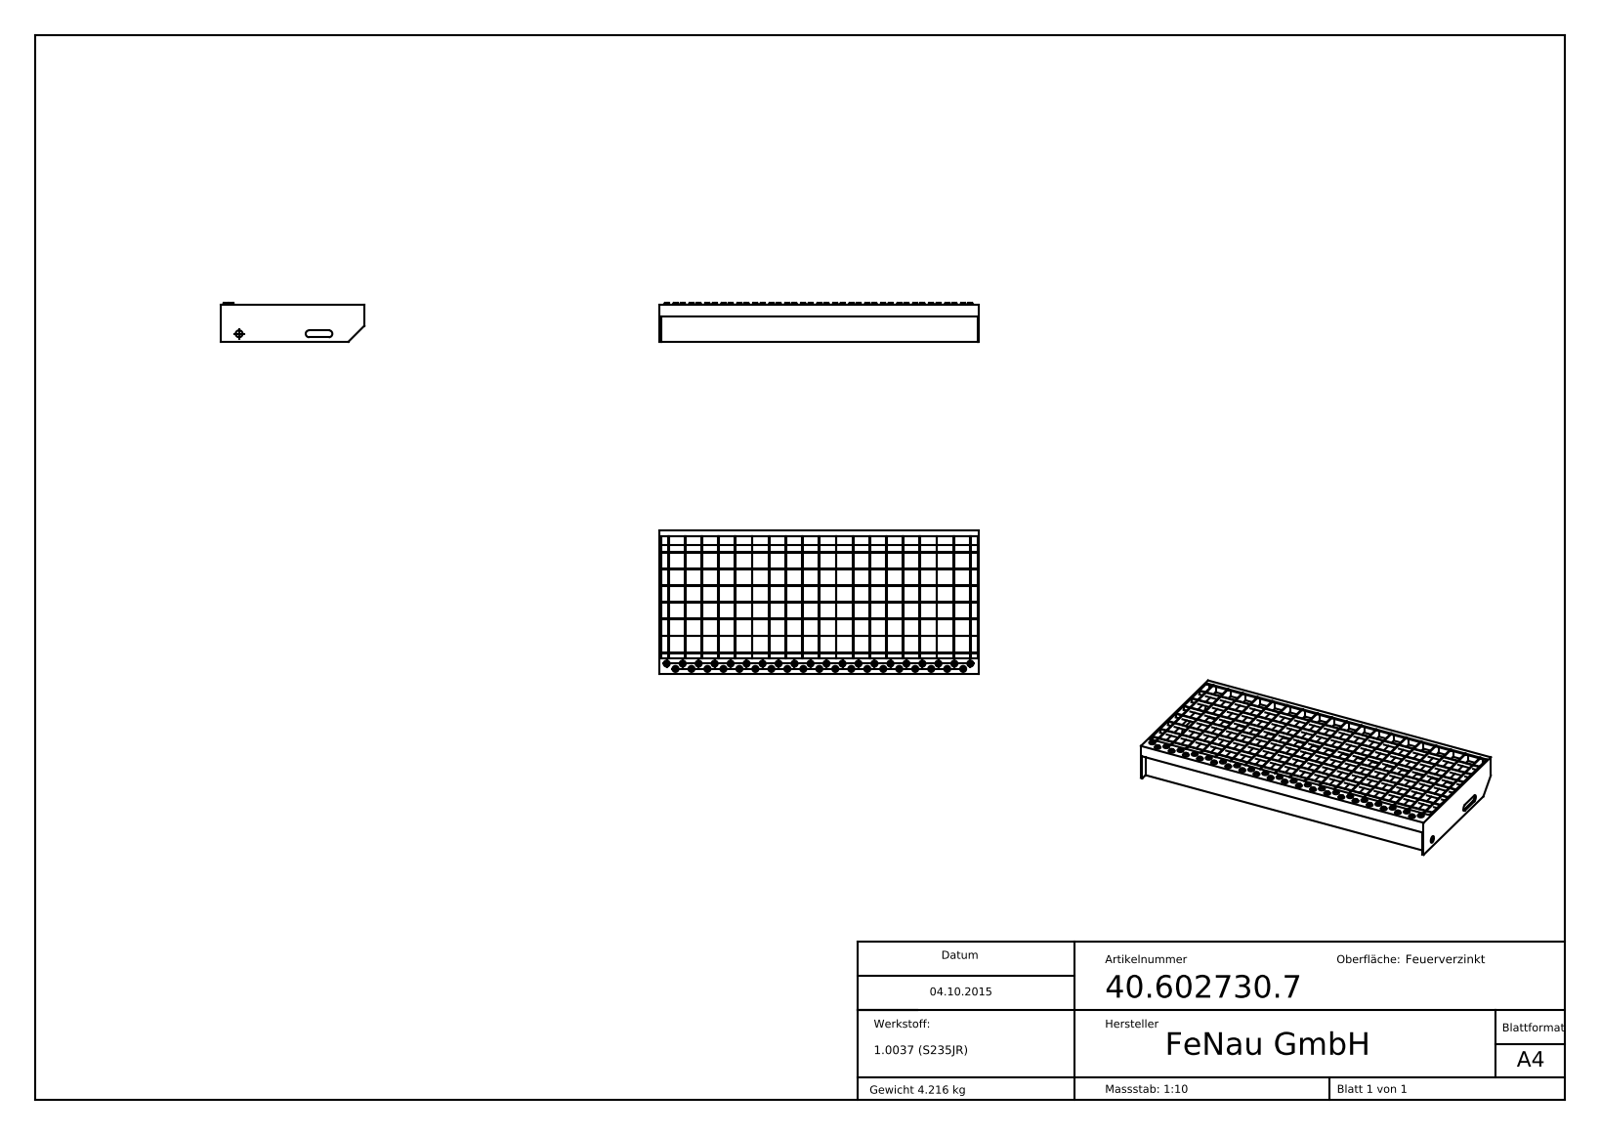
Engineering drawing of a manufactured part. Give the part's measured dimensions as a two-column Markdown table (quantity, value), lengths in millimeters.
| quantity | value |
| --- | --- |
| part name | 40.602730.7 |
| STEP written by | SolidWorks 2015 (CONFIG_CONTROL_DESIGN) |
| units | millimeters |
| bodies | 18 solids, 667 faces (412 planar, 88 cylindrical, 167 other) |
| overall size | 600 × 270 × 72.67 |
| volume | 540 534 mm³ |
| surface area | 609 199 mm² |
| round holes (diameter × count) | 7 × 39, 13 × 1 |
| partial cylindrical surfaces (radius × count) | 6.5 × 2 |
| main face-to-face distances | 2, 31.5, 63, 1.5, 33, 30, 94.5, 61.5, 64.5, 3 |
| hole center spacings | 30, 60, 90, 120, 150, 180, 210, 240 |
